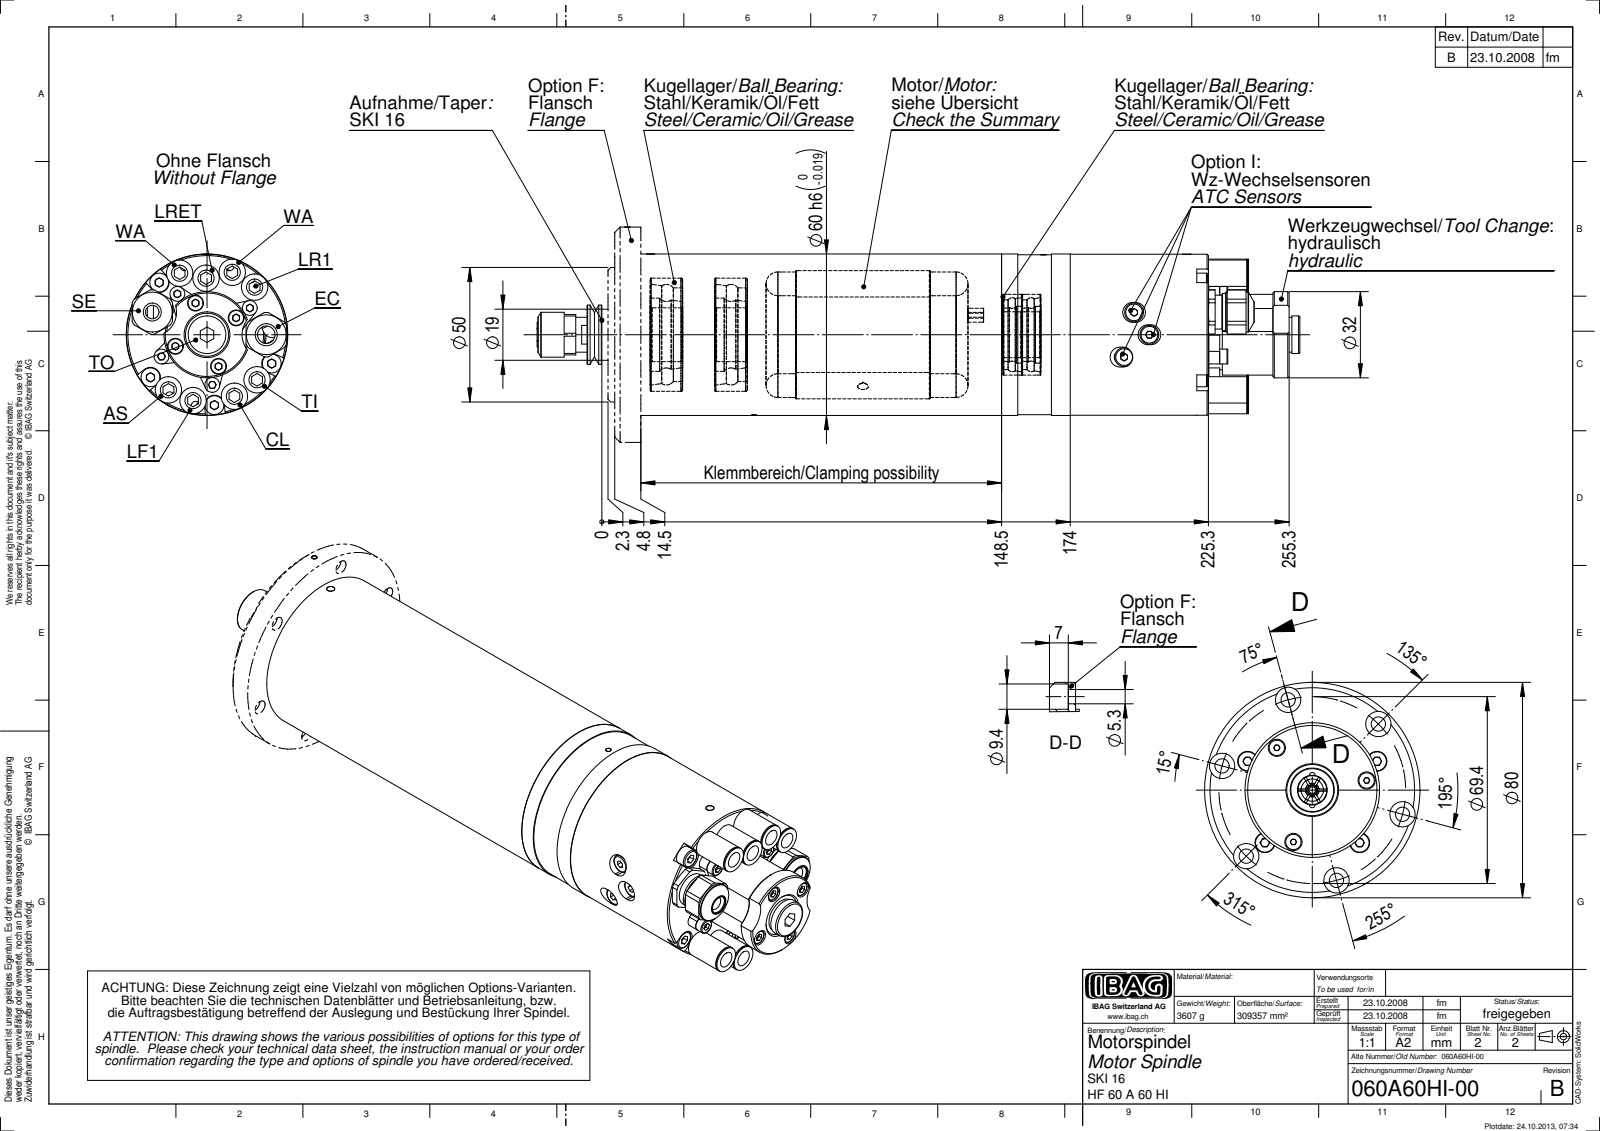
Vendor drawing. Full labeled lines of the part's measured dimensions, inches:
Part name (STEP PRODUCT): 060A60HI-00B
STEP written by: SolidWorks 2009 (CONFIG_CONTROL_DESIGN)
Units: inches
Bodies: 0 solids, 619 faces (291 planar, 208 cylindrical, 120 other)
Overall size (bounding box): 11.156 × 2.362 × 2.362
Round holes (diameter × count): ⌀0.236 ×8, ⌀0.232 ×4, ⌀0.079 ×2, ⌀0.165 ×1, ⌀0.197 ×1, ⌀0.256 ×1, ⌀0.264 ×1, ⌀0.323 ×1
Round bosses / shafts (diameter × count): ⌀0.276 ×9, ⌀0.386 ×8, ⌀0.224 ×3, ⌀0.217 ×3, ⌀0.583 ×2, ⌀0.543 ×2, ⌀0.496 ×2, ⌀2.362 ×1
Partial cylindrical surfaces — rounded edges, fillets, slot ends (radius × count): R0.146 ×14, R0.325 ×2, R0.354 ×2, R0.059 ×1, R0.63 ×1
Main face-to-face distances: 0.382, 0.098, 8.78, 0.48, 8.681, 8.299, 5.756, 5.657, 5.276, 3.024
Hole centre spacings: 0.984, 0.493, 0.393, 0.494, 0.696, 0.866, 1.446, 1.476
